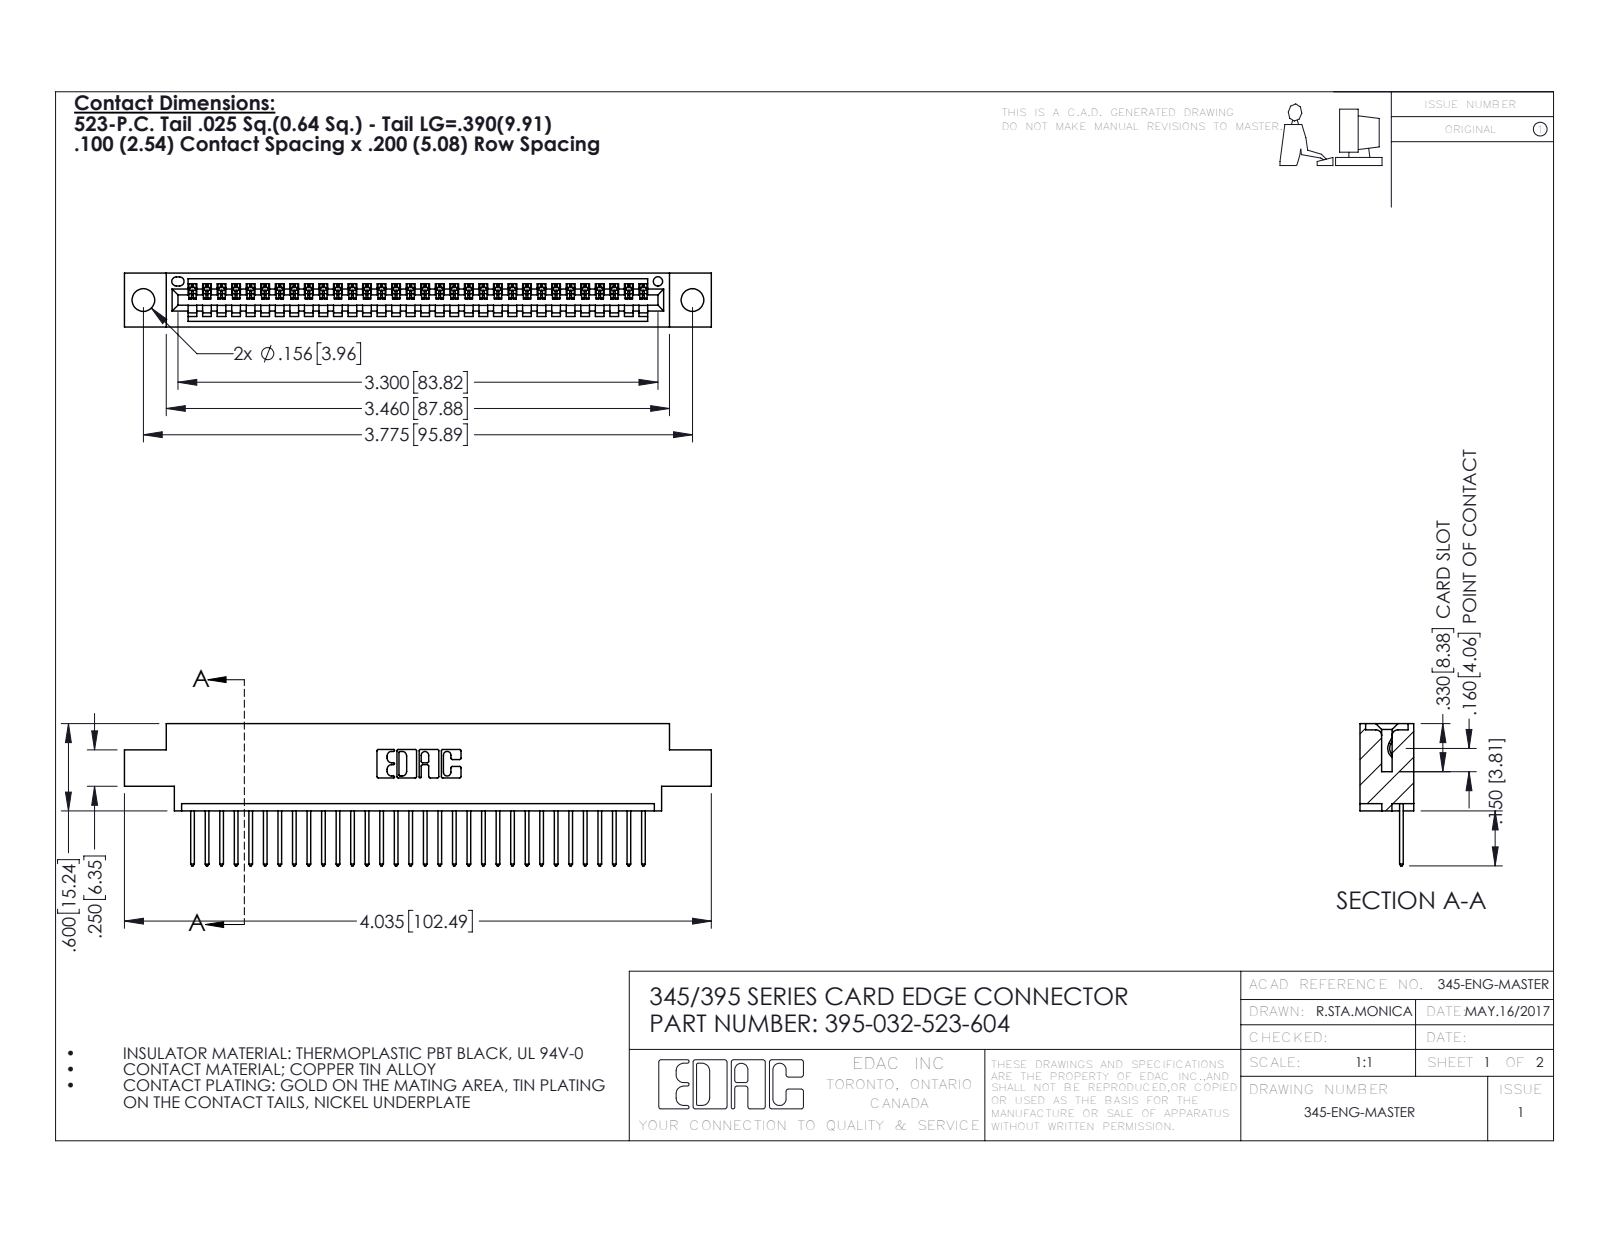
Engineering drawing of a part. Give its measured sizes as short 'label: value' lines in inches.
name: 345-292-001_345-293-123; 395-032-523-604; 345 Part_0.170 Offset - 0.156 Dia-TH
written by: SolidWorks 2016 (CONFIG_CONTROL_DESIGN)
unit: in
bodies: 33 solids, 1986 faces (1364 planar, 622 cylindrical, 0 other)
size: 4.035 × 0.977 × 0.37
volume: 0.576 in³; area: 19.19 in²
holes: 2× ⌀0.156, 1× ⌀0.064
rounds: 64× R0.006, 64× R0.01, 22× R0.01, 6× R0.007, 6× R0.031, 3× R0.026, 2× R0.031, 2× R0.04
face distances: 0.298, 0.072, 0.37, 0.2, 0.098, 0.272, 0.025, 0.225, 0.175, 0.149
hole spacings: 0.27, 3.54, 3.775
